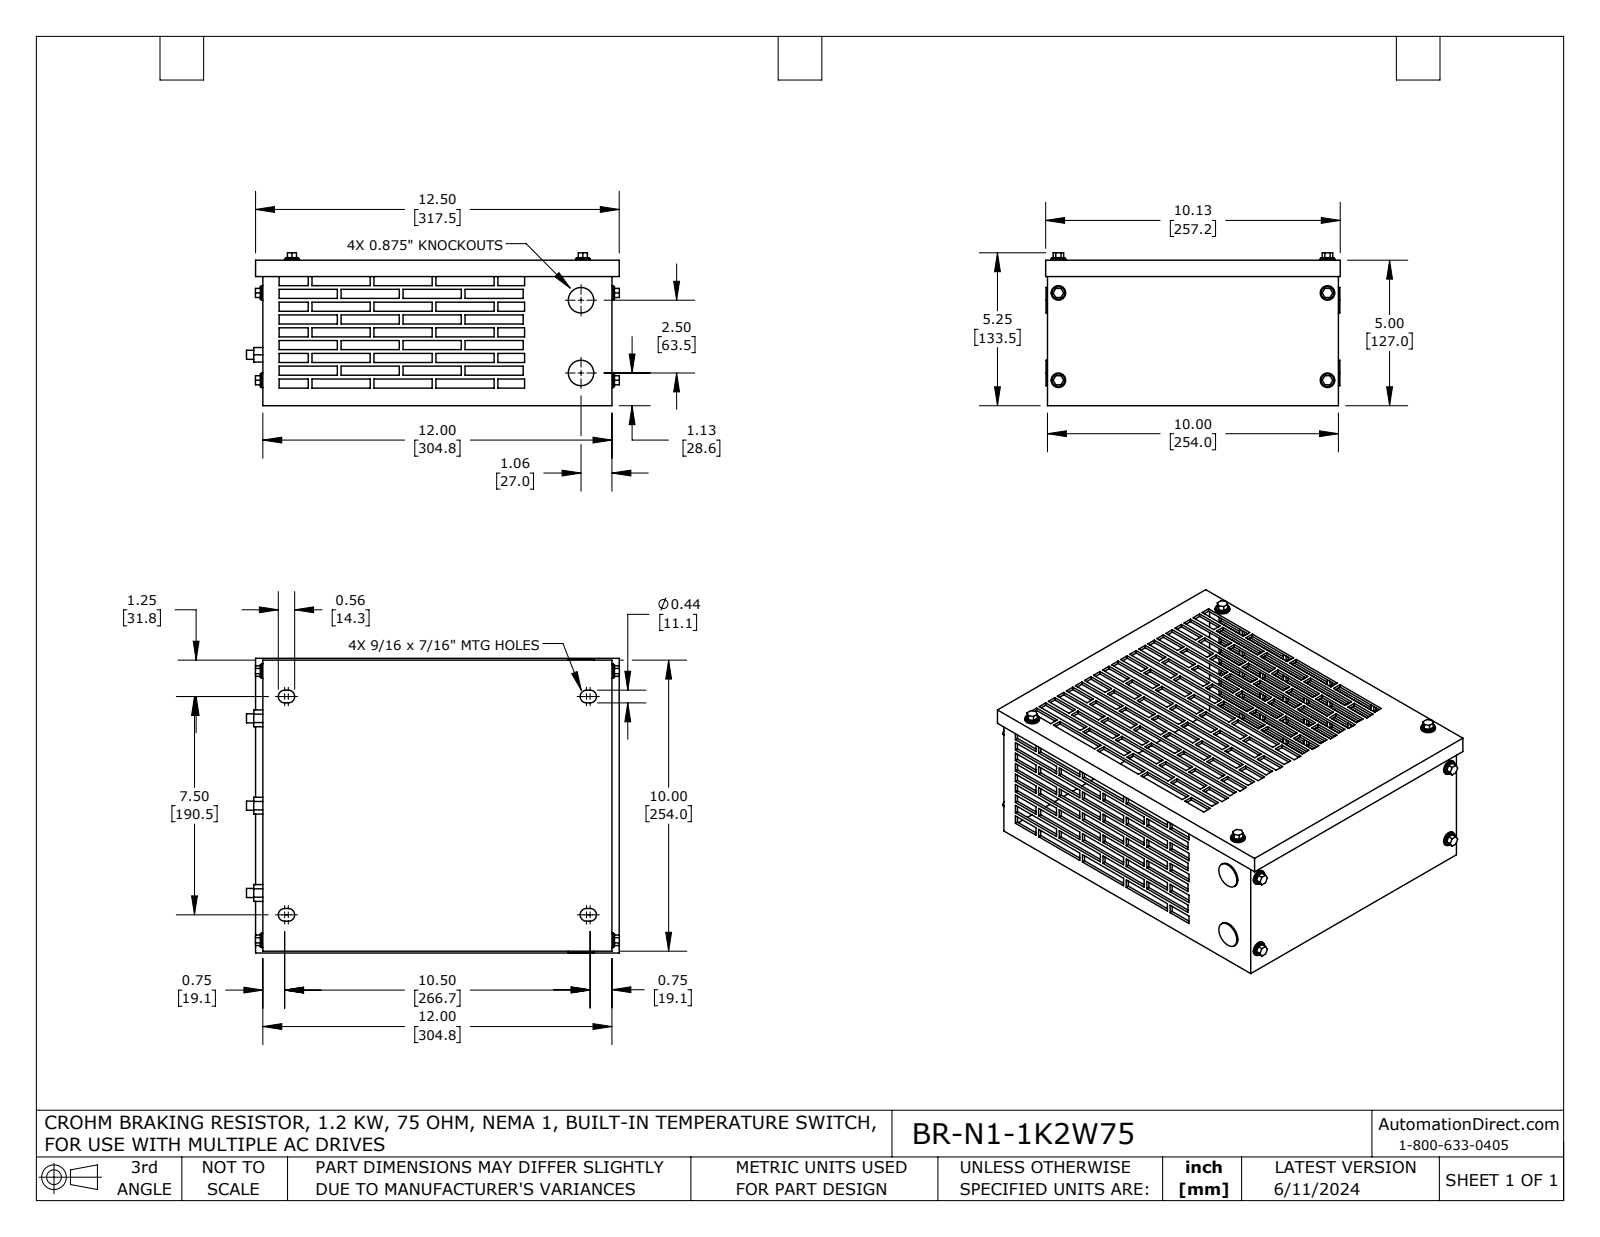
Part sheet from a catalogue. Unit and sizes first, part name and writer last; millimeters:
Units: millimetres
Overall size (bounding box): 325.6 × 257.2 × 133.5
Round holes (diameter × count): ⌀6.4 ×8, ⌀19.1 ×2
Round bosses / shafts (diameter × count): ⌀12.7 ×8, ⌀11.1 ×8, ⌀8 ×3, ⌀22.2 ×2
Partial cylindrical surfaces — rounded edges, fillets, slot ends (radius × count): R5.6 ×8
Main face-to-face distances: 2.5, 124.5, 302.3, 127, 121.9, 251.5, 304.8, 299.7, 254, 248.9
Hole centre spacings: 235, 76.2, 247, 254, 346, 63.5
Volume: 611 600 mm³ · Surface area: 533 000 mm²
Bodies: 32 solids, 981 faces (879 planar, 102 cylindrical, 0 other)
Part name (STEP PRODUCT): BR-N1-1K2W75
STEP written by: SolidWorks 2021 (AUTOMOTIVE_DESIGN)
